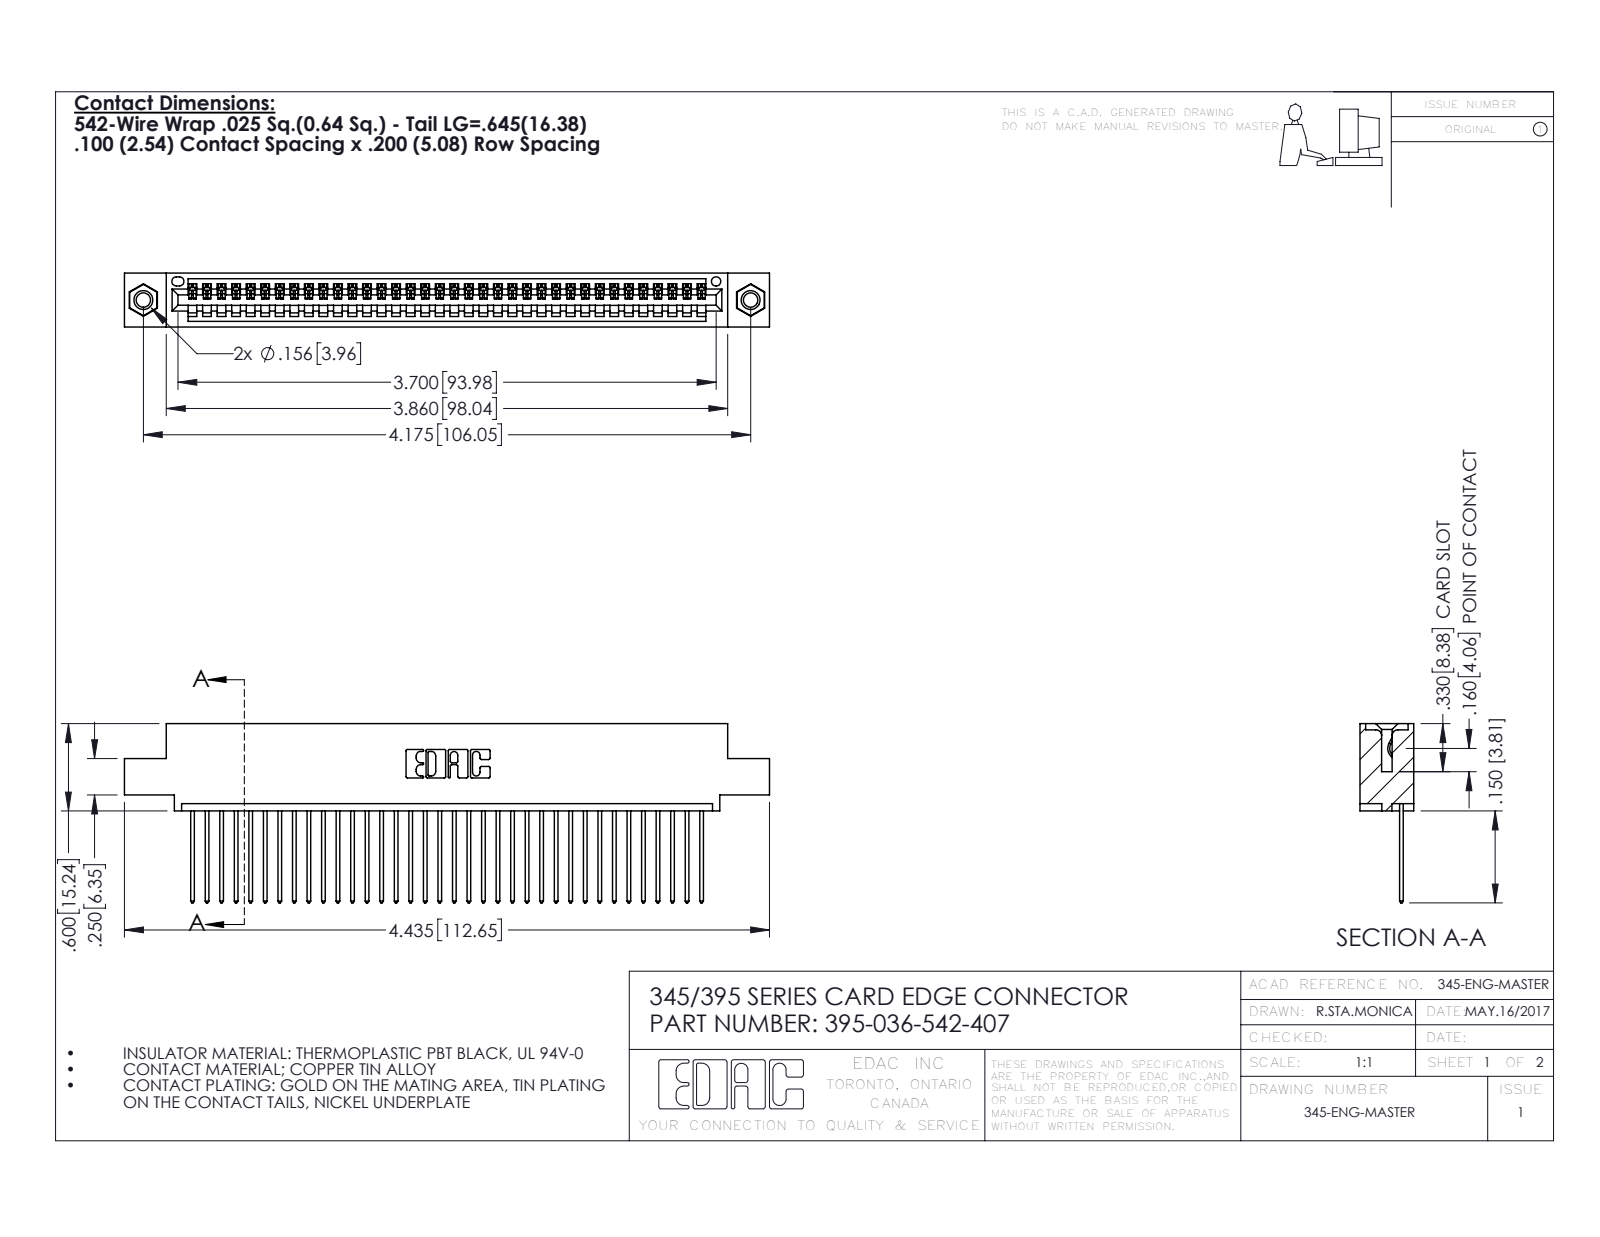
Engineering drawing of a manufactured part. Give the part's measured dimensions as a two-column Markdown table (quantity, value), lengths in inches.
| quantity | value |
| --- | --- |
| part name | 395-036-542-407; 345-250-001_345-250-005-103; 345-292-001_345-293-142; 345 Part_0.110 Offset - 0.156 Dia-TI |
| STEP written by | SolidWorks 2016 (CONFIG_CONTROL_DESIGN) |
| units | inches |
| bodies | 39 solids, 2278 faces (1556 planar, 706 cylindrical, 16 other) |
| overall size | 4.435 × 1.232 × 0.37 |
| volume | 0.65 in³ |
| surface area | 22.76 in² |
| round holes (diameter × count) | 0.098 × 2, 0.125 × 2, 0.156 × 2, 0.064 × 1 |
| round bosses / shafts (diameter × count) | 0.155 × 2 |
| partial cylindrical surfaces (radius × count) | 0.006 × 72, 0.01 × 72, 0.01 × 22, 0.007 × 6, 0.031 × 6, 0.026 × 3, 0.031 × 2, 0.04 × 2 |
| main face-to-face distances | 0.072, 0.298, 0.37, 0.098, 0.272, 0.025, 0.2, 0.225, 0.149, 0.072 |
| hole center spacings | 0.27, 3.939, 4.175 |
